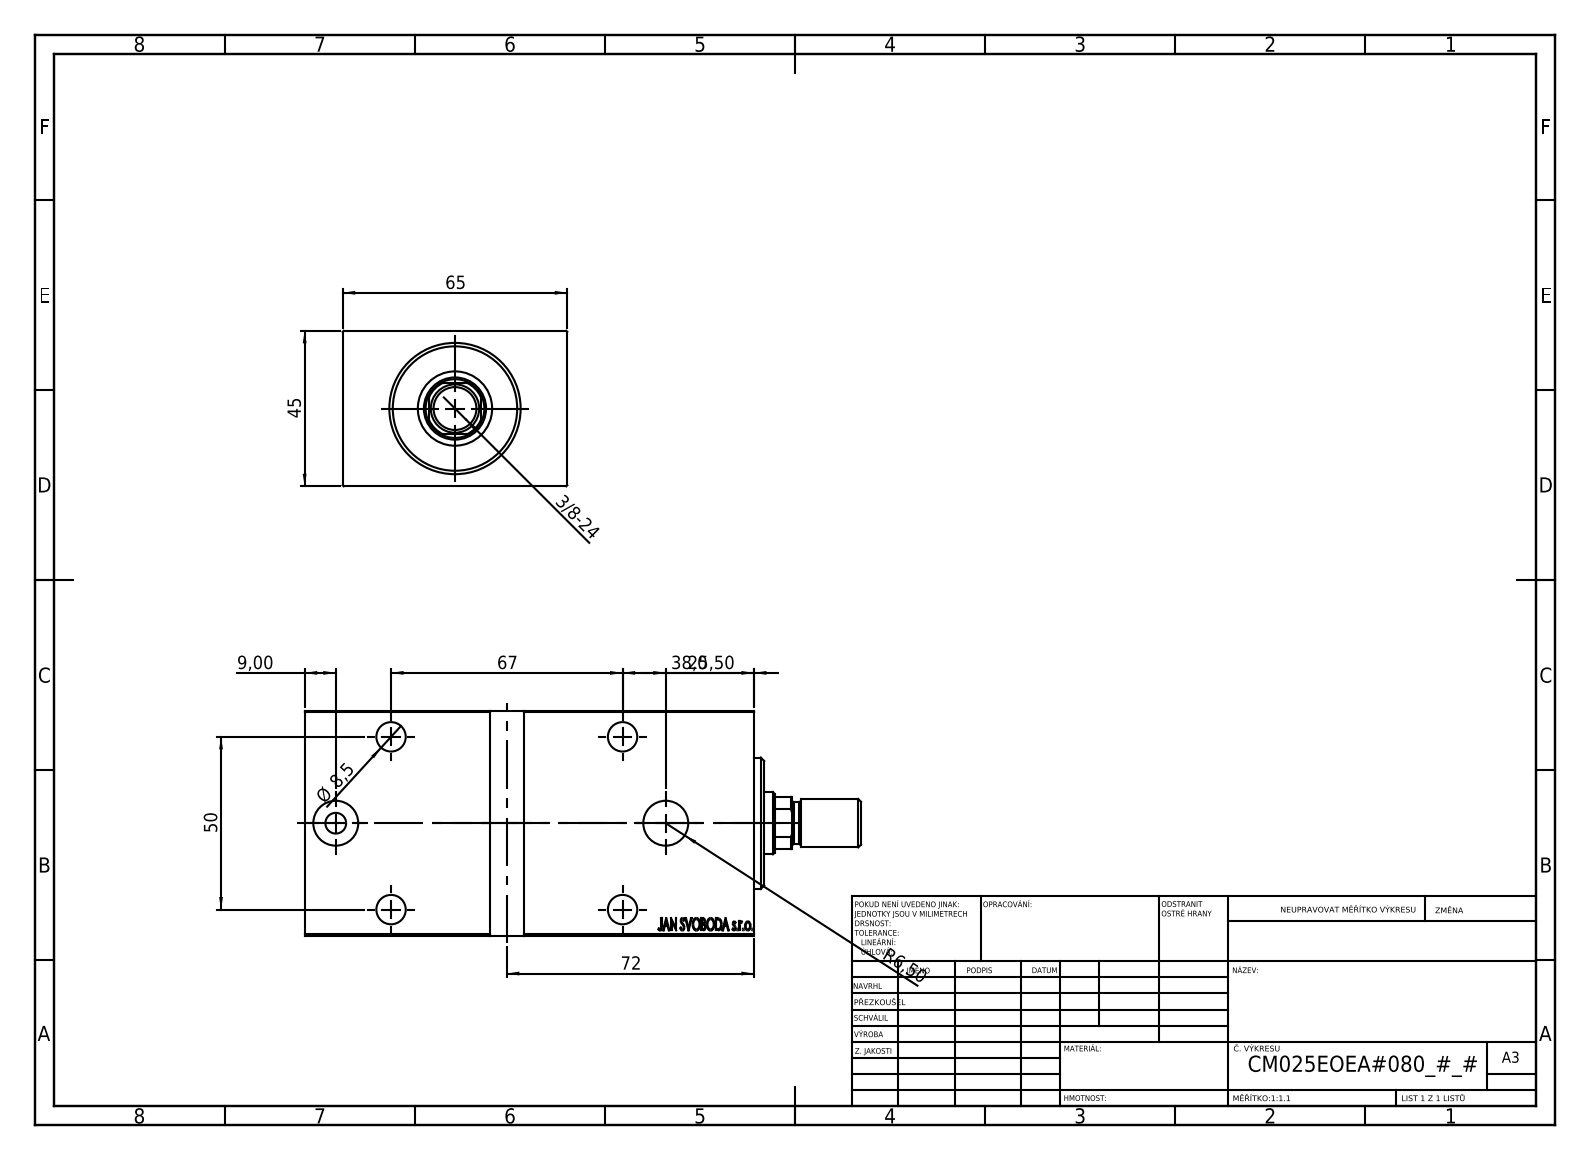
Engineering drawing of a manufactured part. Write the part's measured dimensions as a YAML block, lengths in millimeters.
part_name: "V450CM_VC_B; V450CM_MALE_METRIC; V450CM_E_VCP; V450CM_E_Body"
step_written_by: "SolidWorks 2019 (CONFIG_CONTROL_DESIGN)"
units: millimeters
bodies: {solids: 4, faces: 862, planar: 412, cylindrical: 50, other: 400}
overall_size: [161, 65, 45]
volume: 354649
surface_area: 65345
round_holes:
  - {diameter: 8.5, count: 5}
  - {diameter: 13.5, count: 4}
  - {diameter: 13, count: 2}
  - {diameter: 18, count: 1}
  - {diameter: 21.5, count: 1}
  - {diameter: 25, count: 1}
  - {diameter: 35, count: 1}
round_bosses_or_shafts:
  - {diameter: 38, count: 1}
  - {diameter: 27, count: 1}
  - {diameter: 14, count: 1}
  - {diameter: 12, count: 1}
  - {diameter: 6, count: 1}
partial_cylinders:
  - {radius: 8.5, count: 1}
face_to_face_distances: [45, 65, 130, 6, 124, 8, 5, 125, 119, 3]
hole_center_spacings: [27.95, 29.68, 50, 67, 83.34, 83.6, 86.68, 95.5]
